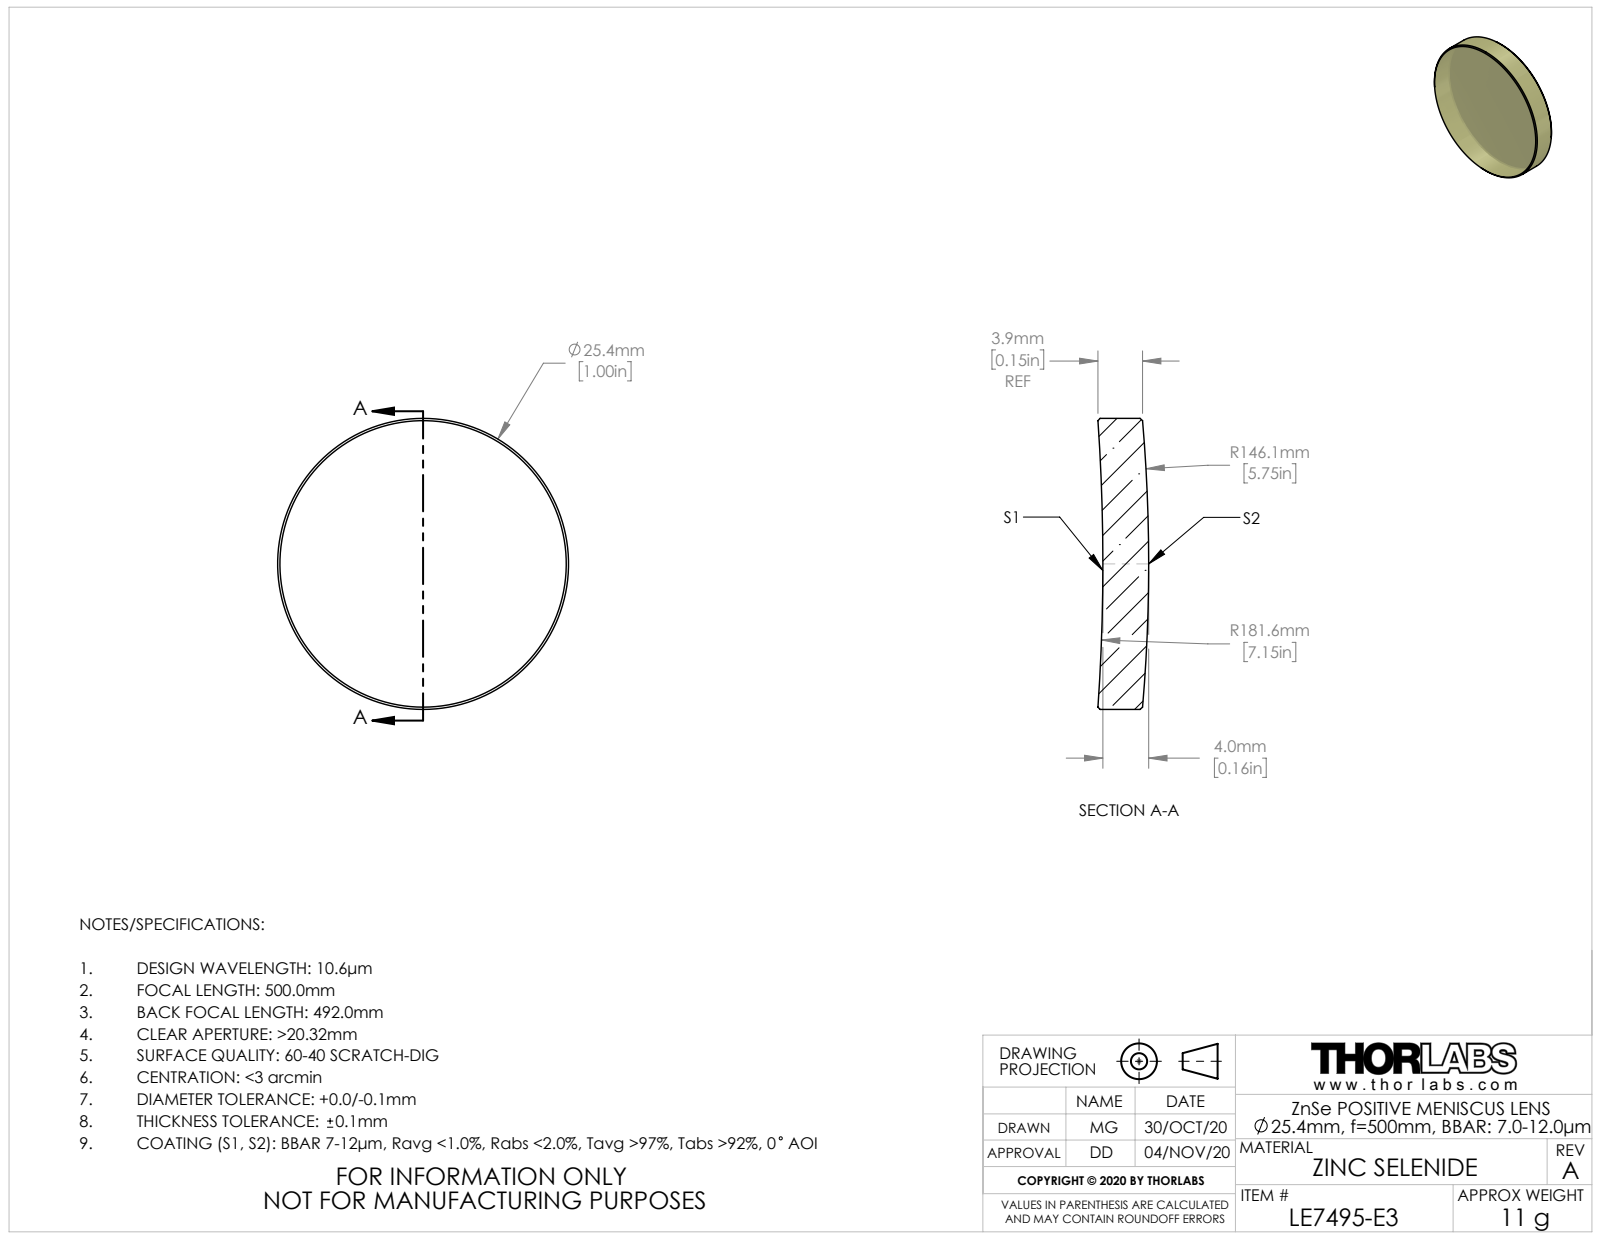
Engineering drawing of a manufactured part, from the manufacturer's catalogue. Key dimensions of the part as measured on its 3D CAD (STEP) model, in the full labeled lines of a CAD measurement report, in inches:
Part name (STEP PRODUCT): TTN225633-E0W
STEP written by: SolidWorks 2018 (CONFIG_CONTROL_DESIGN)
Units: inches
Bodies: 1 solid, 10 faces (0 planar, 2 cylindrical, 8 other)
Overall size (bounding box): 1 × 1 × 0.174
Volume: 0.122 in³ · Surface area: 2.026 in²
Round bosses / shafts (diameter × count): ⌀1 ×1
